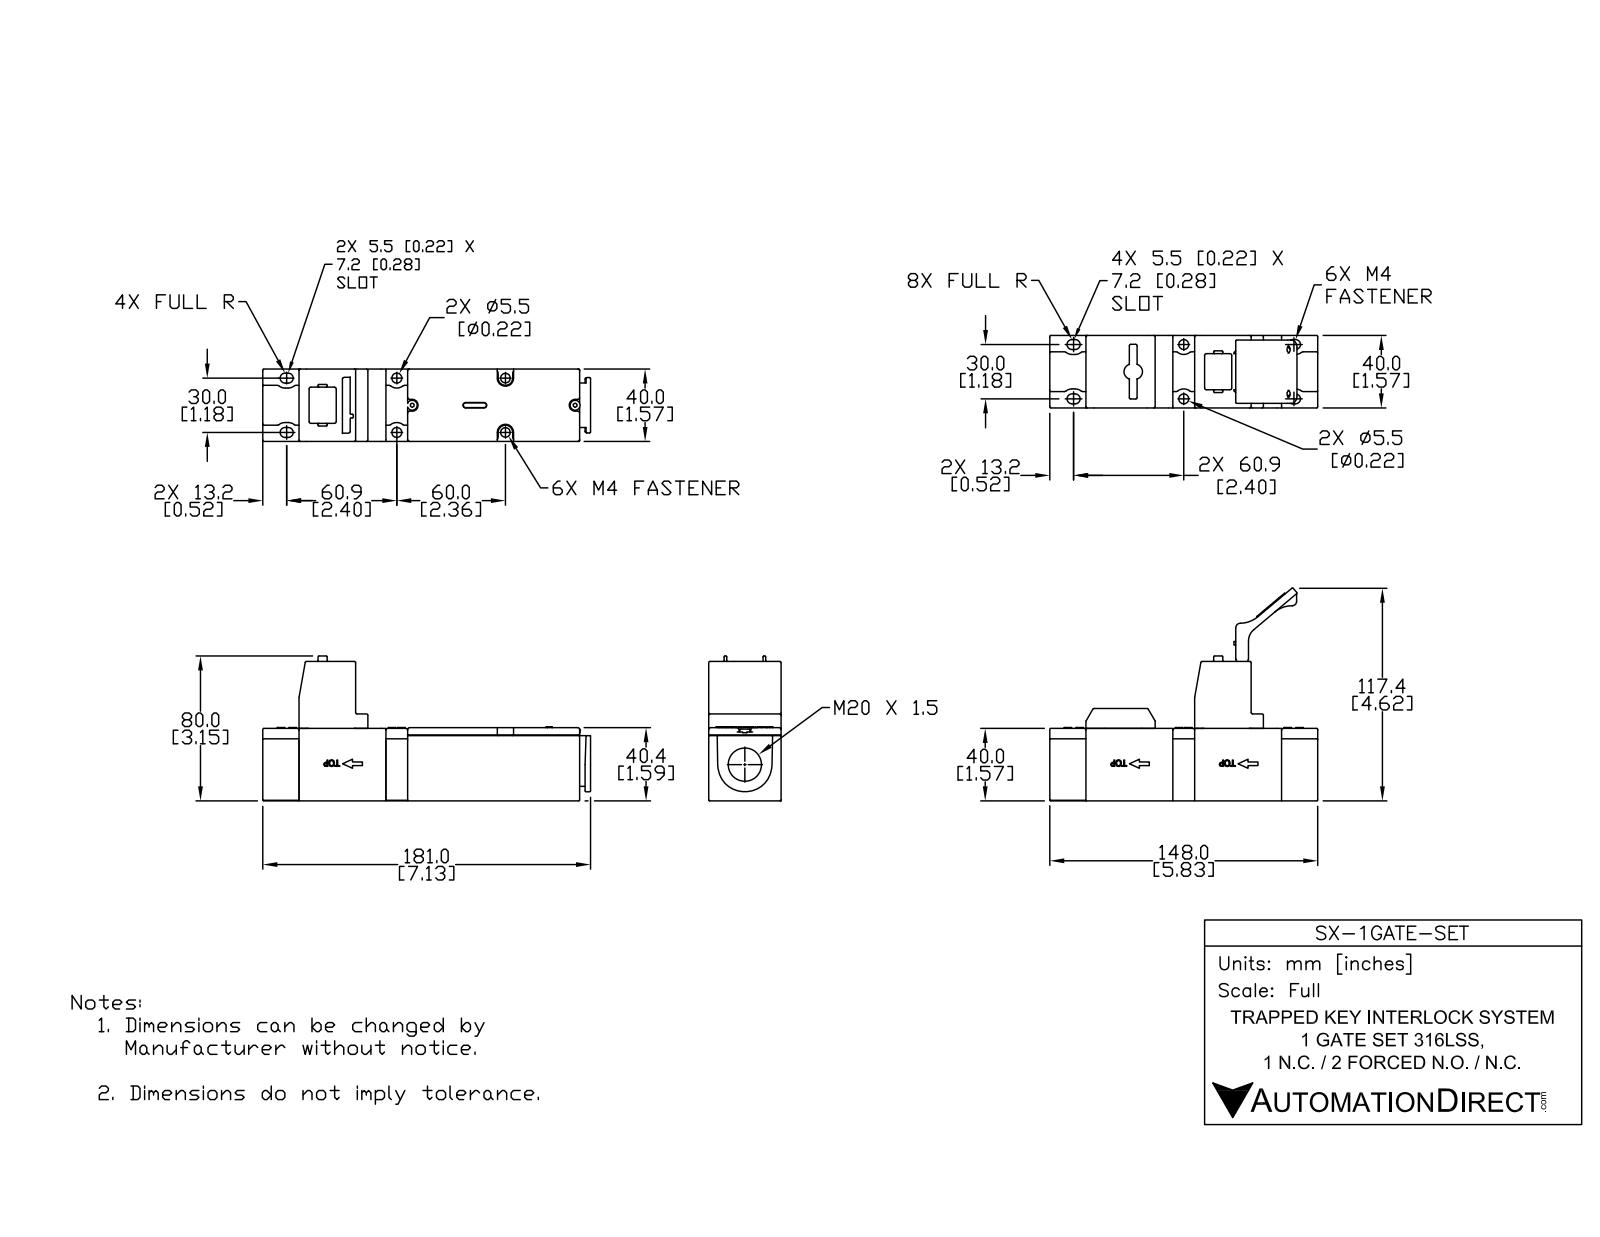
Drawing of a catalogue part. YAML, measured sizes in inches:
part_name: "SX-1GATE-SET"
step_written_by: "SolidWorks 2017 (AUTOMOTIVE_DESIGN)"
units: inches
bodies: {solids: 15, faces: 5282, planar: 2278, cylindrical: 809, other: 2195}
overall_size: [10.149, 6.545, 3.906]
volume: 37.83
surface_area: 183.8
round_holes:
  - {diameter: 0.157, count: 8}
  - {diameter: 0.217, count: 4}
  - {diameter: 0.079, count: 2}
  - {diameter: 0.097, count: 2}
  - {diameter: 0.097, count: 2}
  - {diameter: 0.209, count: 2}
  - {diameter: 0.134, count: 1}
  - {diameter: 0.723, count: 1}
round_bosses_or_shafts:
  - {diameter: 0.394, count: 2}
  - {diameter: 0.217, count: 2}
  - {diameter: 0.161, count: 1}
partial_cylinders:
  - {radius: 0.02, count: 324}
  - {radius: 0.039, count: 84}
  - {radius: 0.03, count: 64}
  - {radius: 0.006, count: 44}
  - {radius: 0.018, count: 36}
  - {radius: 0.079, count: 21}
  - {radius: 0.217, count: 16}
  - {radius: 0.108, count: 12}
face_to_face_distances: [1.575, 4.961, 1.063, 2.362, 1.89, 3.425, 2.953, 0.472, 3.386, 0.787]
hole_center_spacings: [0.571, 1.181, 0.965, 3.197, 3.486, 5.073, 5.531, 6.028]
